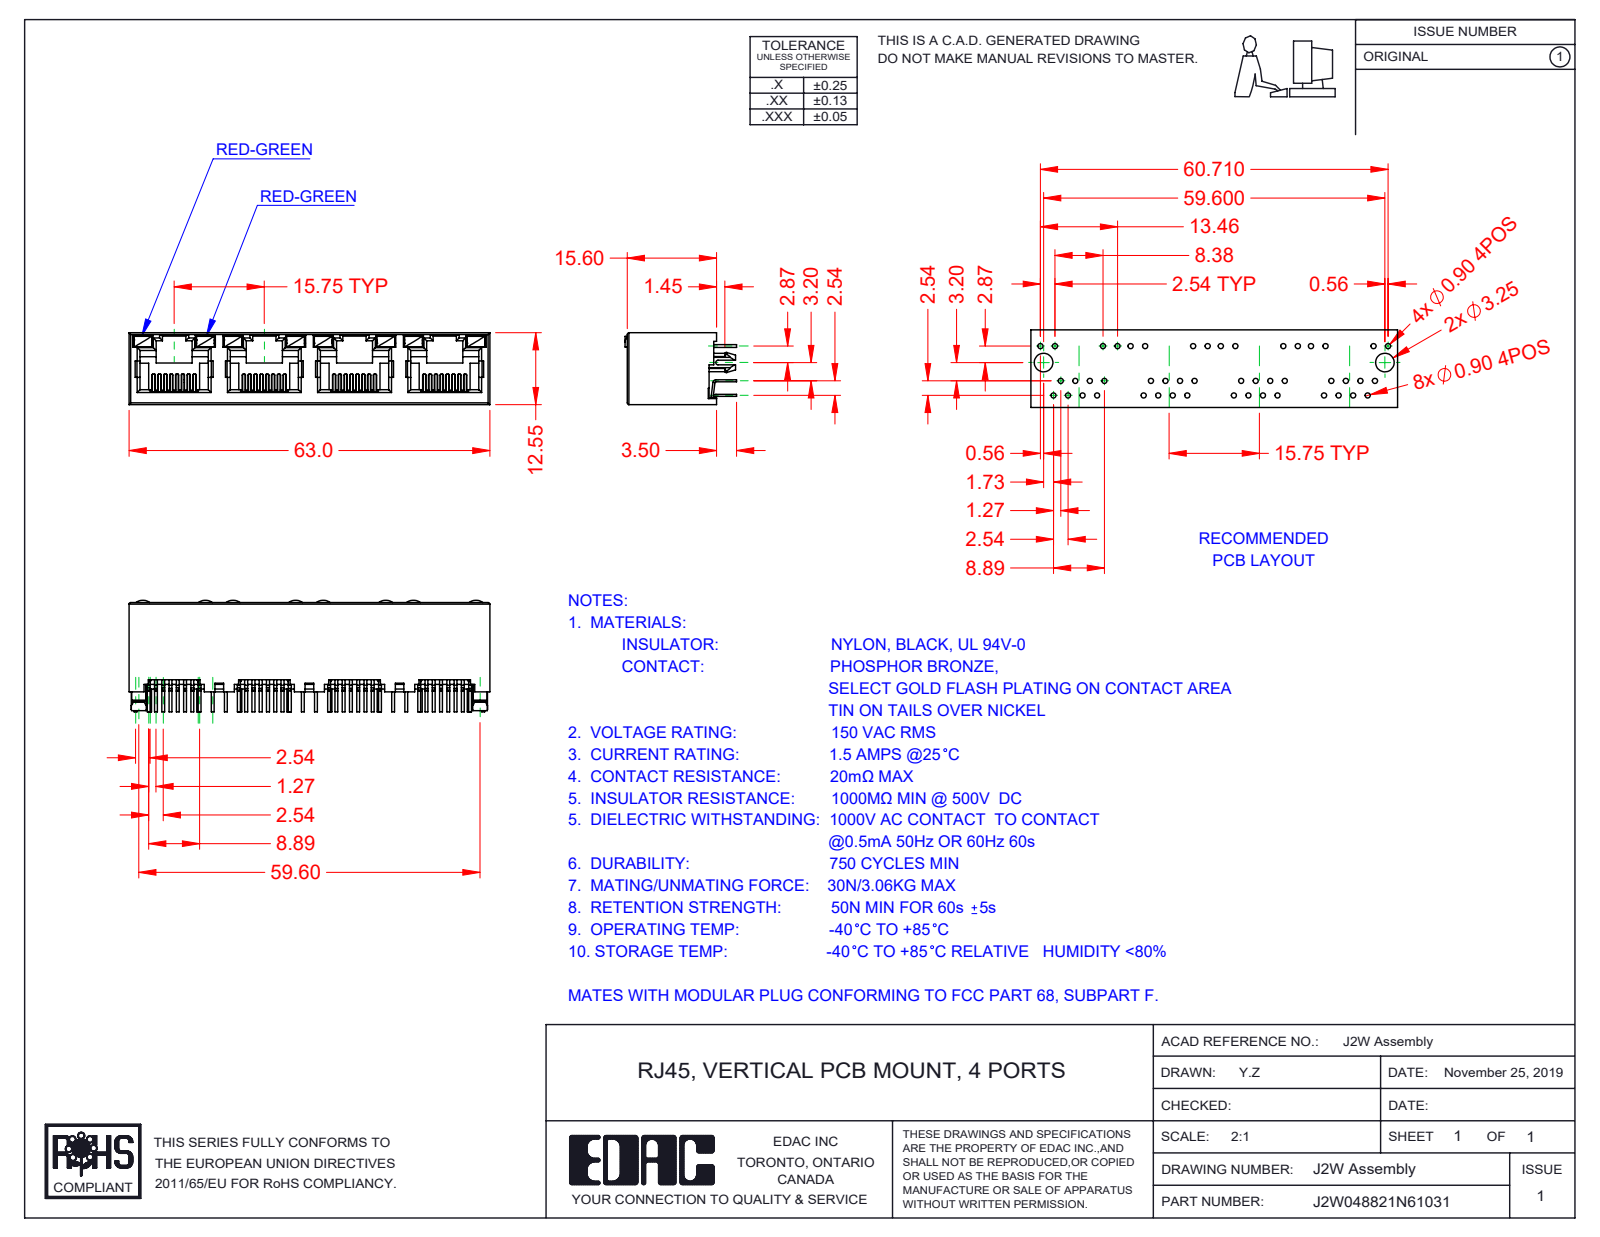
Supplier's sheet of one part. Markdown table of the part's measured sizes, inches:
| quantity | value |
| --- | --- |
| part name | 2W LED RH_6-Red-Green; 2W Contact Lock; 2W Contacts; J2W048821N66131 (+2 more) |
| STEP written by | SolidWorks 2016 (CONFIG_CONTROL_DESIGN) |
| units | inches |
| bodies | 45 solids, 3143 faces (2600 planar, 485 cylindrical, 58 other) |
| overall size | 2.48 × 0.768 × 0.494 |
| volume | 0.326 in³ |
| surface area | 20.37 in² |
| partial cylindrical surfaces (radius × count) | 0.006 × 64, 0.008 × 29, 0.02 × 28, 0.012 × 14, 0.018 × 8, 0.079 × 8, 0.01 × 2, 0.059 × 2 |
| main face-to-face distances | 0.494, 0.469, 0.026, 0.62, 0.014, 0.059, 0.031, 0.024, 0.445, 1.24 |
